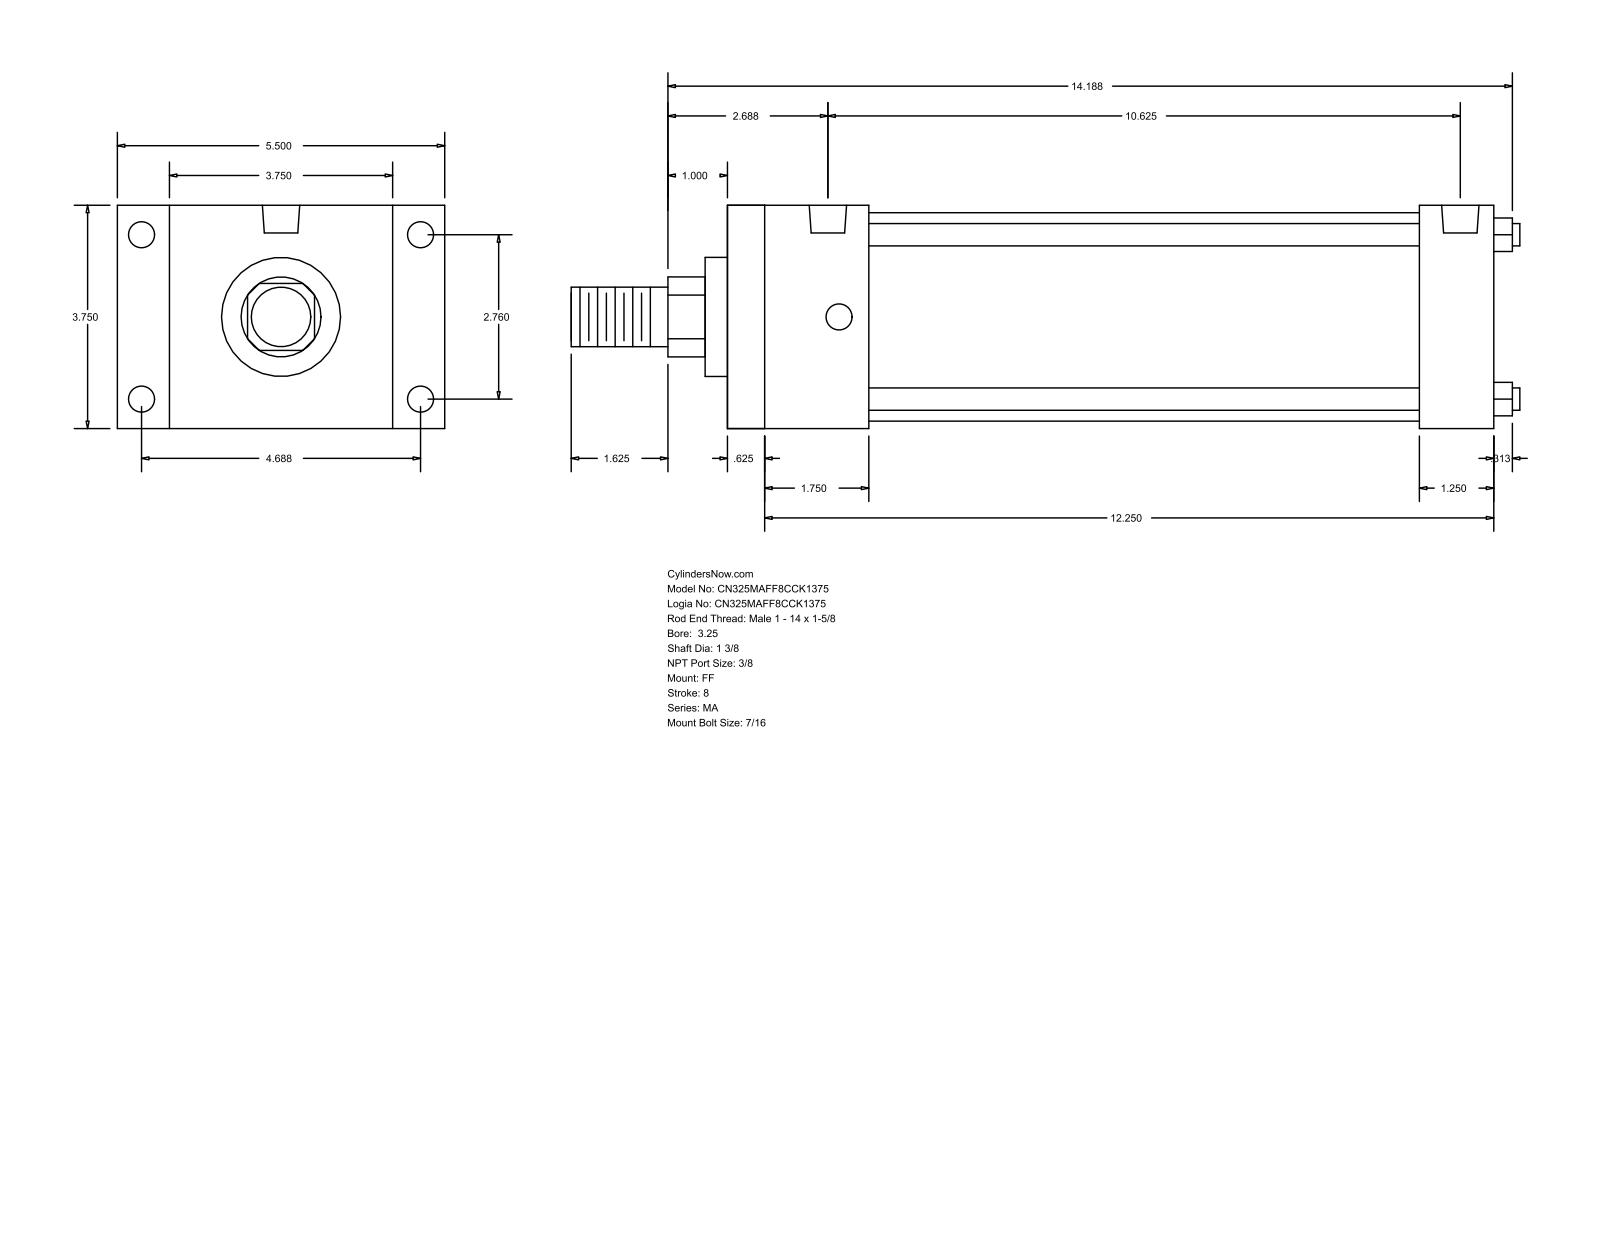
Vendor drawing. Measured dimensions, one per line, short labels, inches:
name: MA_FF__0325_1.375
written by: GSSL Pune (CONFIG_CONTROL_DESIGN)
unit: in
bodies: 0 solids, 92 faces (64 planar, 28 cylindrical, 0 other)
size: 15.937 × 5.5 × 3.75
holes: 8× ⌀0.437, 2× ⌀0.627
bosses: 4× ⌀0.375, 1× ⌀3.5, 1× ⌀2, 1× ⌀1.375, 1× ⌀1
rounds: 1× R0.672
face distances: 3.75, 12.875, 0.625, 12.25, 0.875, 4.625, 2.375, 11.625, 1.75, 11
hole spacings: 2.76, 4.687, 5.439, 10.25, 0.187, 0.188, 10.437, 10.438
